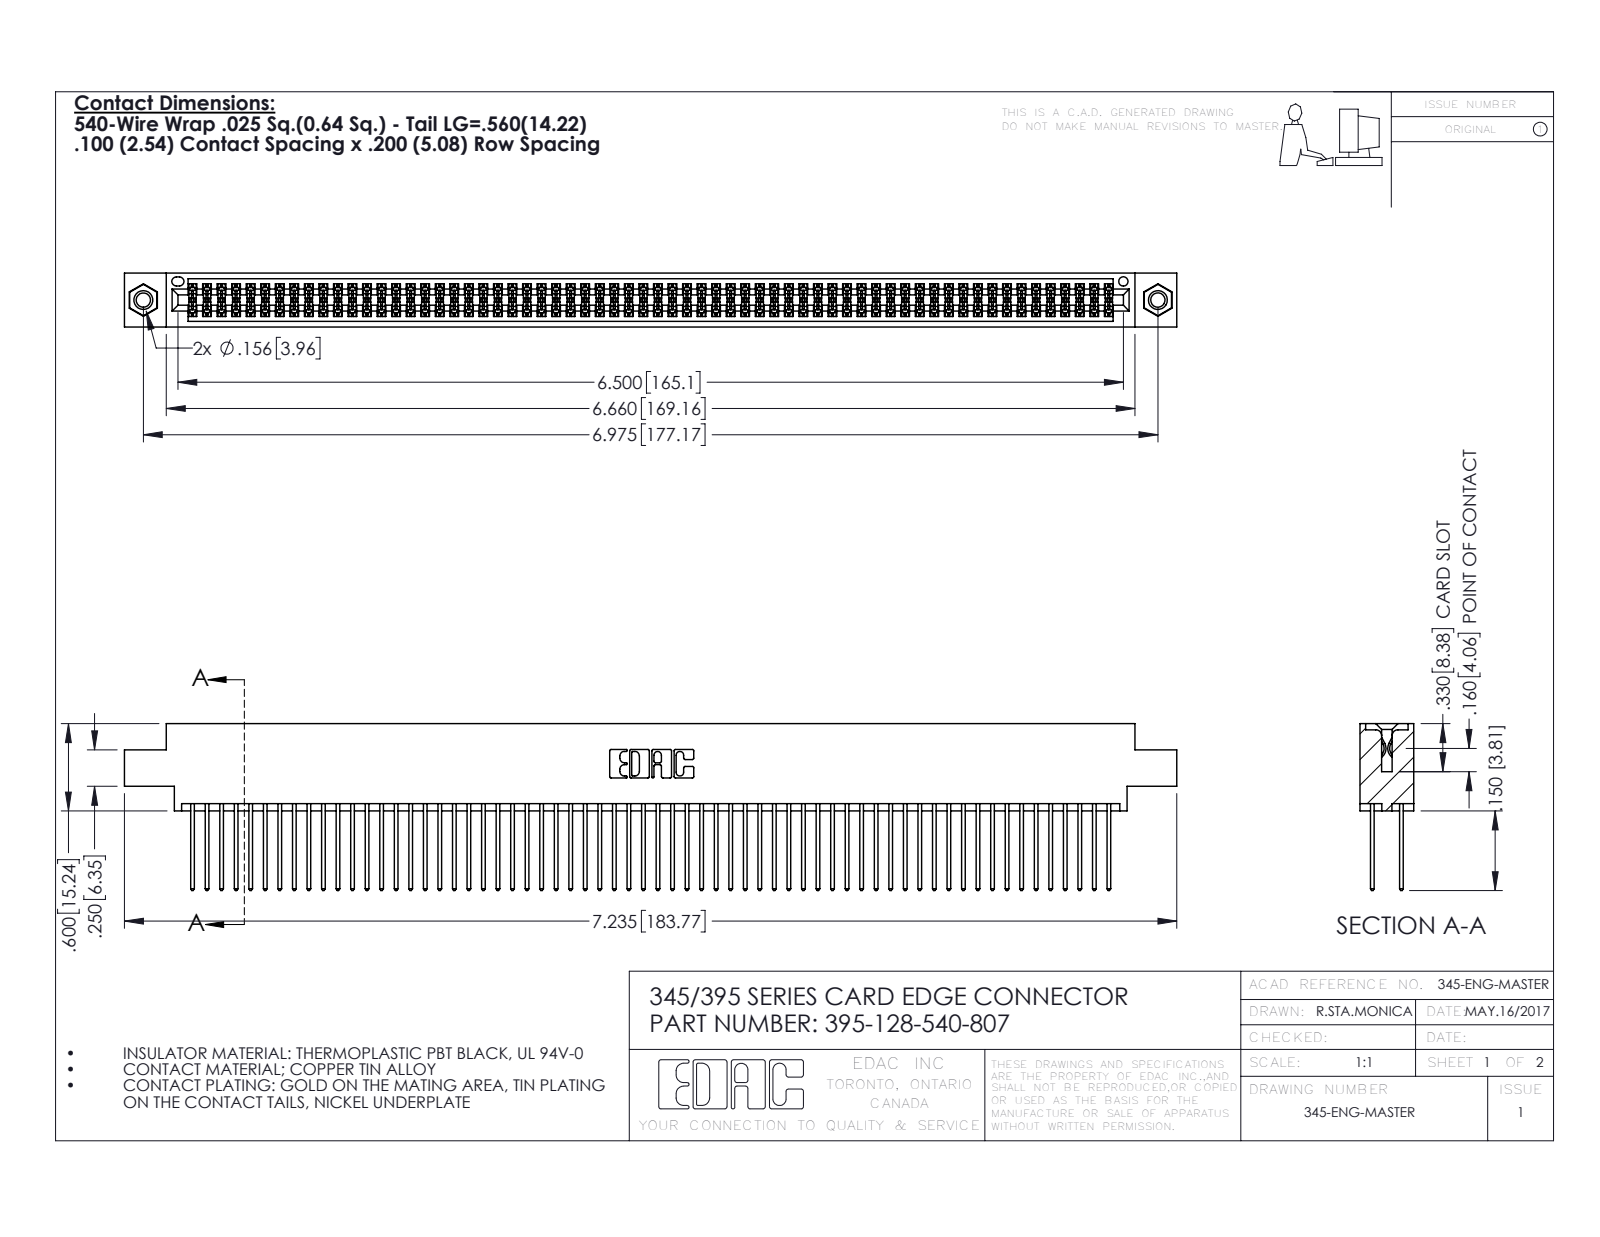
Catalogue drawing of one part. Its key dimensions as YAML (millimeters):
part_name: "395-128-540-807; 345 Part_0.170 Offset - 0.156 Dia-TI; 345-250-001_345-250-005-103; 345-292-001_345-293-140"
step_written_by: "SolidWorks 2016 (CONFIG_CONTROL_DESIGN)"
units: millimeters
bodies: {solids: 131, faces: 6590, planar: 4340, cylindrical: 2234, other: 16}
overall_size: [183.8, 29.1, 9.4]
volume: 18420
surface_area: 30070
round_holes:
  - {diameter: 2.5, count: 2}
  - {diameter: 3.2, count: 2}
  - {diameter: 4, count: 2}
  - {diameter: 1.6, count: 1}
round_bosses_or_shafts:
  - {diameter: 3.9, count: 2}
partial_cylinders:
  - {radius: 0.2, count: 192}
  - {radius: 0.3, count: 128}
  - {radius: 0.3, count: 22}
  - {radius: 0.2, count: 6}
  - {radius: 0.8, count: 6}
  - {radius: 0.7, count: 3}
  - {radius: 0.4, count: 2}
  - {radius: 0.5, count: 2}
face_to_face_distances: [1.8, 7.6, 5.1, 2.5, 6.9, 0.6, 9.4, 5.7, 4.4, 3.8]
hole_center_spacings: [6.9, 171.2, 177.2]
